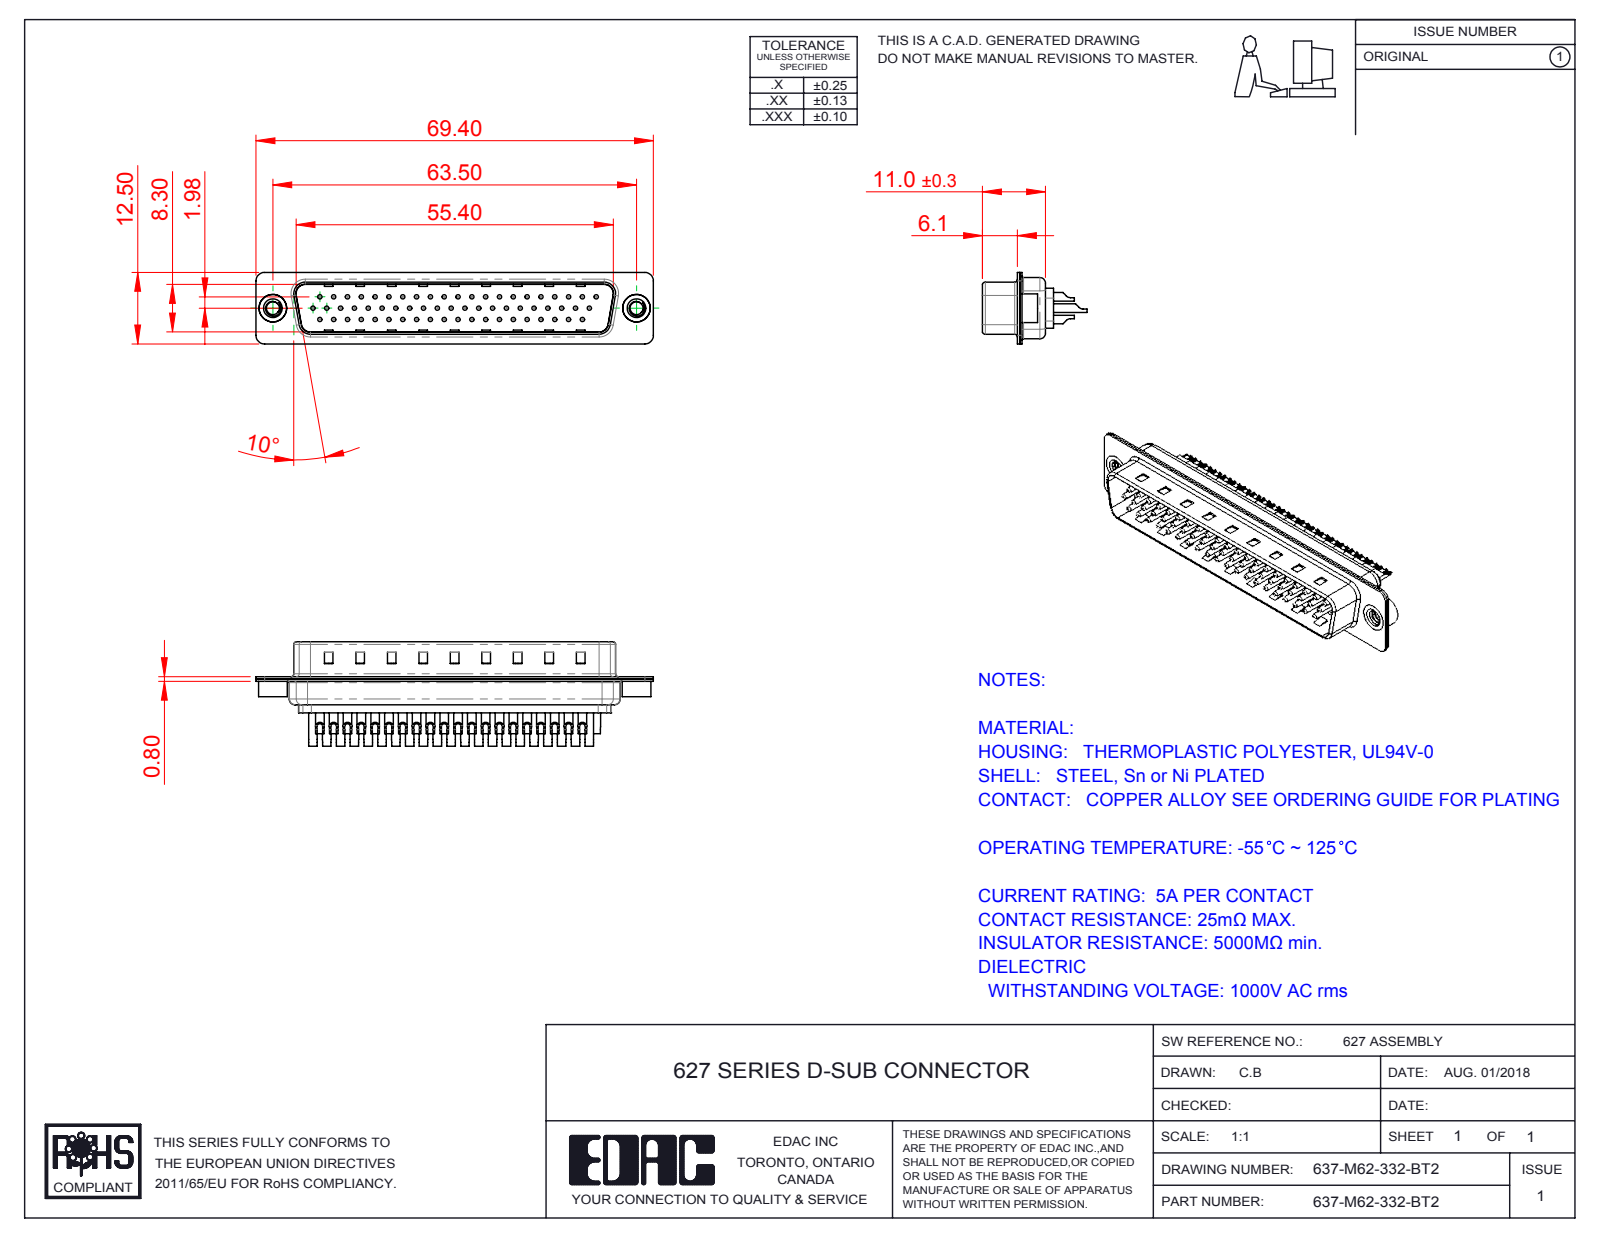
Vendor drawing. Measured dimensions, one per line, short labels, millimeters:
name: 637M Contact Row 3_32; 637M Housing_62 Contacts; 637M Contact Row 1_32; 637M Contact Row 2_32 (+4 more)
written by: SolidWorks 2016 (CONFIG_CONTROL_DESIGN)
unit: mm
bodies: 67 solids, 2706 faces (761 planar, 1133 cylindrical, 812 other)
size: 69.4 × 18.25 × 12.5
volume: 4 122 mm³; area: 12 177 mm²
holes: 62× ⌀0.75, 62× ⌀1, 62× ⌀1.6, 62× ⌀2, 2× ⌀2.26, 2× ⌀4, 2× ⌀4.8
bosses: 62× ⌀1.5, 2× ⌀5, 2× ⌀4.9
rounds: 16× R1.5, 12× R2, 8× R0.5, 8× R1.6, 7× R1, 4× R0.25, 4× R0.6, 4× R0.65
face distances: 0.4, 0.8, 9.5, 9.1, 8.7, 9.9, 0.75, 0.35, 1.2, 1.5
hole spacings: 7.24, 2.32, 2.41, 4.13, 9.65, 4.83, 14.48, 11.04
